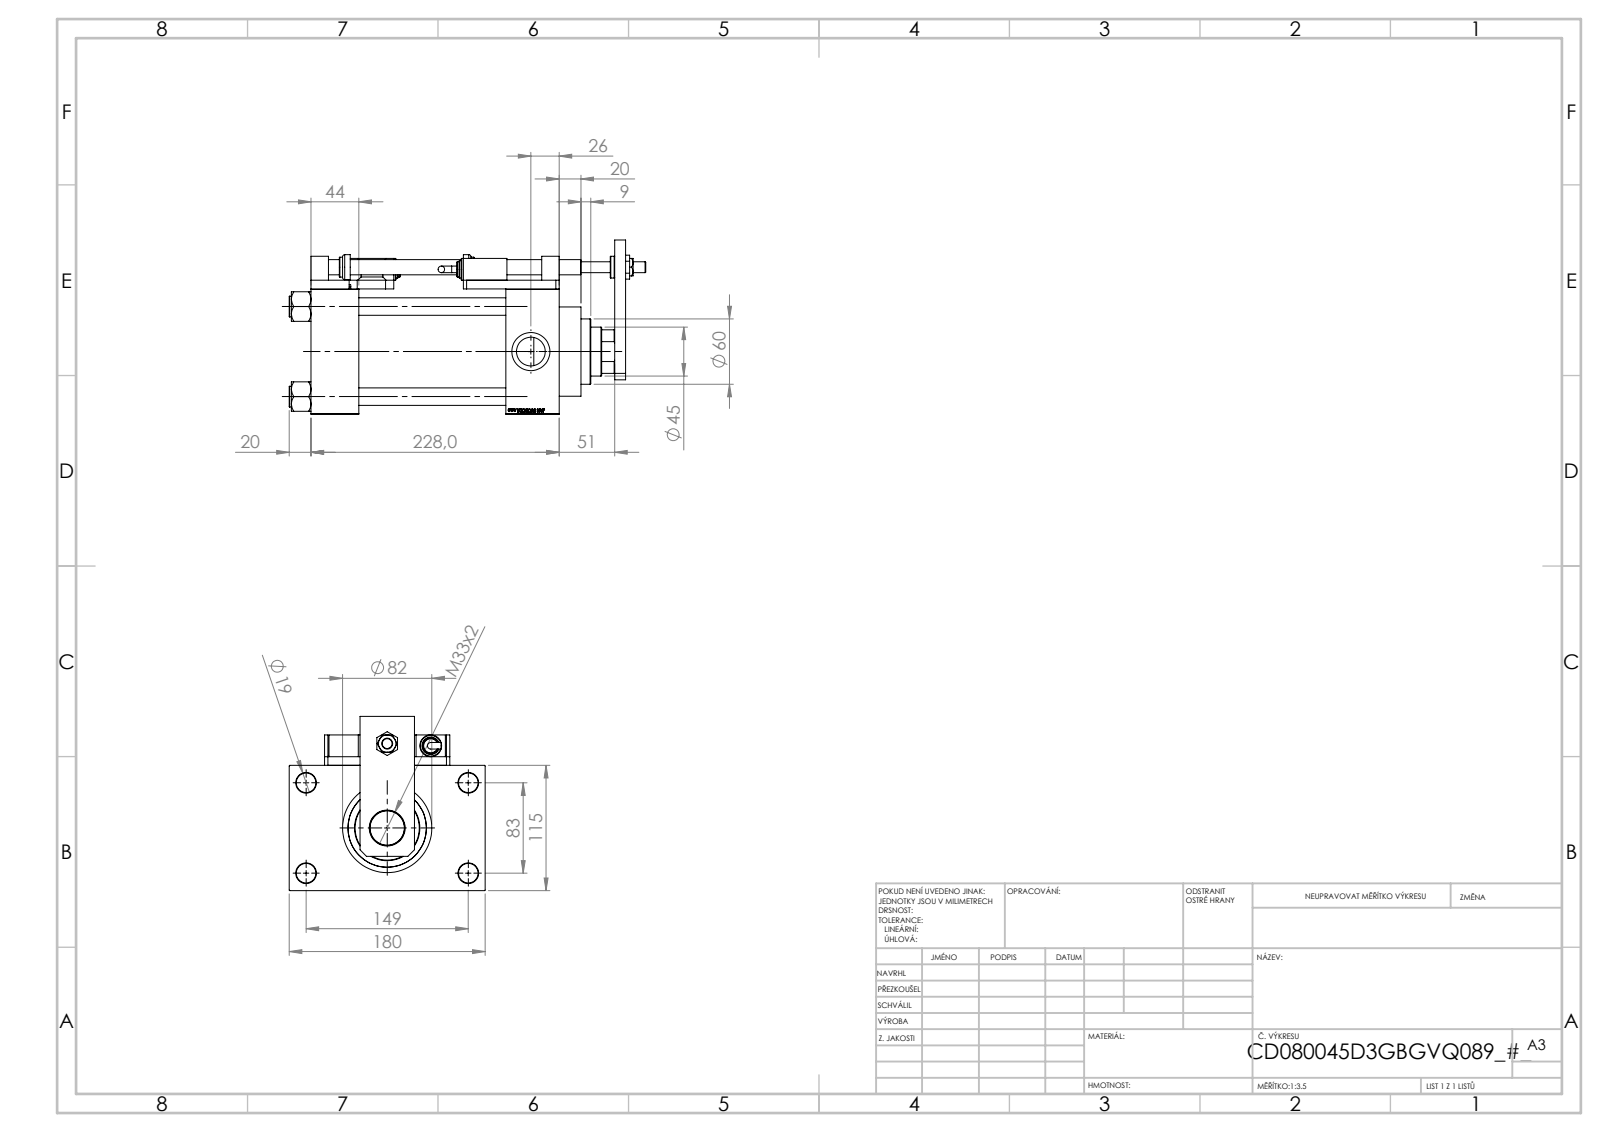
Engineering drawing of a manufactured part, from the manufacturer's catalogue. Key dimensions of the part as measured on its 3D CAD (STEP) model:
Part name (STEP PRODUCT): V215CD_SWITCH_Q_ZARAZKA; V215CD_D_Body; V215CD_SWITCH_Q_NUT10; V215CD_VCP_D (+7 more)
STEP written by: SolidWorks 2019 (CONFIG_CONTROL_DESIGN)
Units: millimetres
Bodies: 26 solids, 1480 faces (714 planar, 167 cylindrical, 599 other)
Overall size (bounding box): 327.5 × 180 × 160
Volume: 2 512 000 mm³ · Surface area: 462 514 mm²
Round holes (diameter × count): ⌀8.5 ×4, ⌀13.5 ×4, ⌀16 ×4, ⌀18 ×4, ⌀26.44 ×4, ⌀35 ×4, ⌀7 ×3, ⌀10 ×1, ⌀14 ×1, ⌀31.5 ×1, ⌀33 ×1, ⌀45 ×1
Round bosses / shafts (diameter × count): ⌀19 ×4, ⌀20 ×3, ⌀16 ×2, ⌀14 ×2, ⌀6 ×2, ⌀86 ×1, ⌀82 ×1, ⌀60 ×1
Partial cylindrical surfaces — rounded edges, fillets, slot ends (radius × count): R7.5 ×4, R22 ×1
Main face-to-face distances: 115, 8, 49, 44, 184, 228, 179, 135, 123, 32.5
Hole centre spacings: 33.15, 58.48, 82.7, 85.28, 89.24, 115.85, 142.43, 21.26
